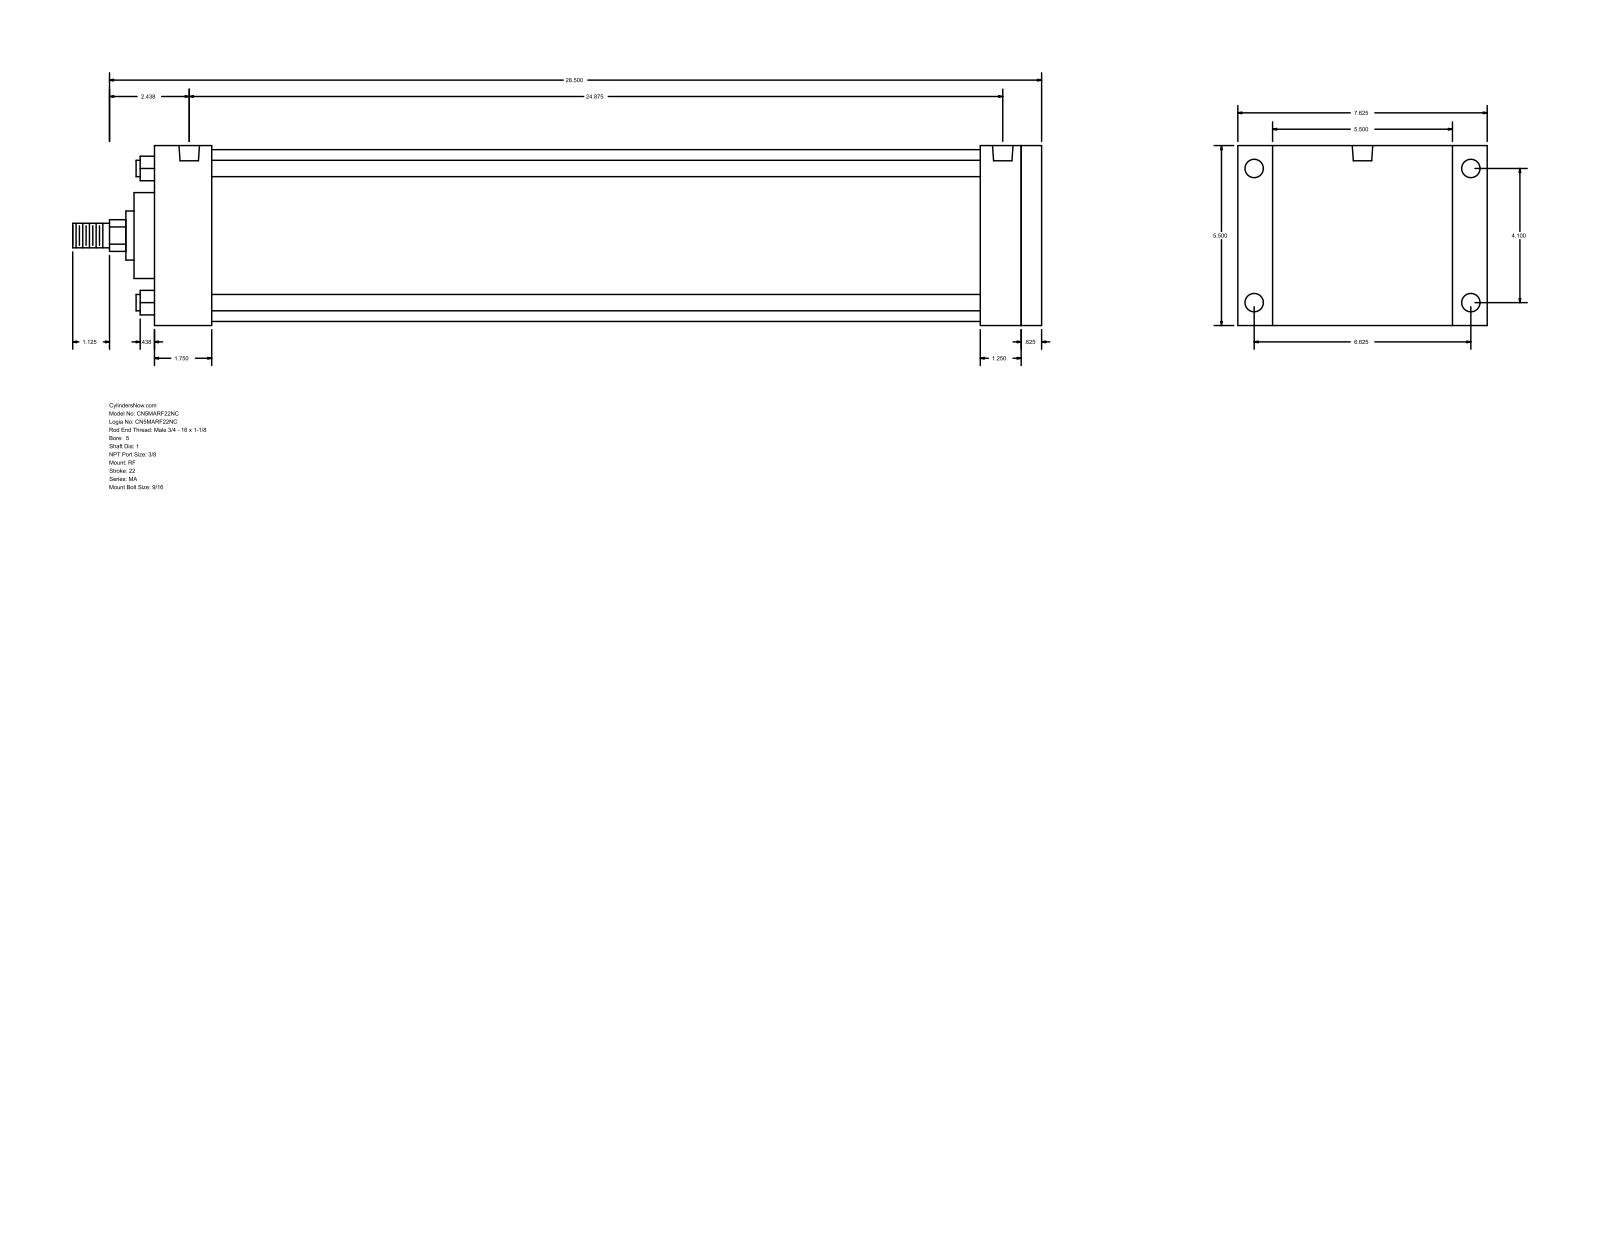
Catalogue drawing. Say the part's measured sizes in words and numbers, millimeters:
The part is named "MA_RF__0500_1". Its 3-D file was written by "GSSL Pune (CONFIG_CONTROL_DESIGN)". It is 0 solids with 94 faces: 65 planar, 29 cylindrical and 0 other. Overall it measures 752.48 by 193.68 by 139.7 millimeters. Round holes: 4 of diameter 11.11, 4 of diameter 14.29, 2 of diameter 15.93. Round bosses or shafts: 4 of diameter 12.7, 1 of diameter 133.35, 1 of diameter 66.67, 1 of diameter 38.1, 1 of diameter 25.4, 1 of diameter 19.05. Partial cylindrical surfaces (rounded edges, fillets, slot ends): 1 of radius 12.29. The main face-to-face distances are 139.7, 688.98, 673.1, 15.88, 44.46, 628.64, 644.52, 641.35, 596.89, 31.75. The hole center spacings are 4.76, 104.14, 168.28, 197.9, 622.31, 627.07, 631.83.
